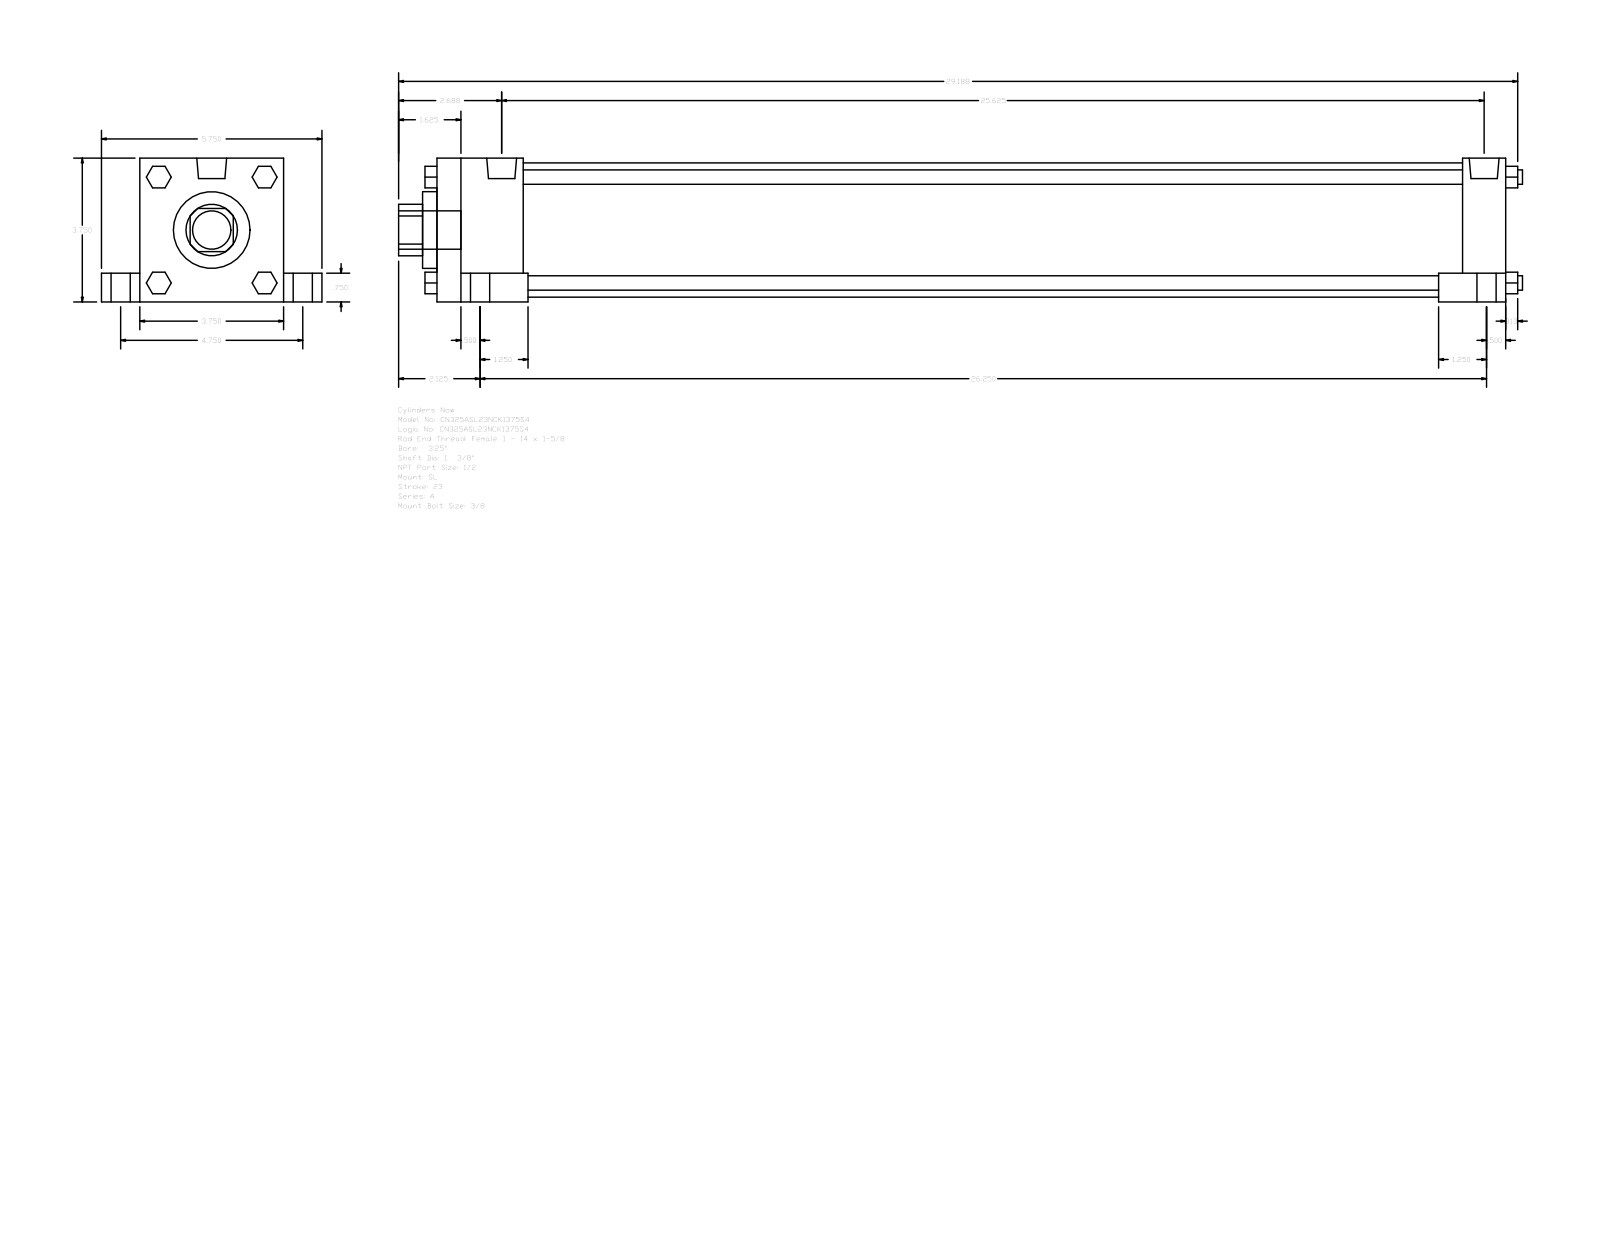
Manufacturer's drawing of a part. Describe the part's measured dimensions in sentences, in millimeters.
The part is named "A_SL__0325_1.375". Its 3-D file was written by "GSSL Pune (CONFIG_CONTROL_DESIGN)". It is 0 solids with 150 faces: 114 planar, 36 cylindrical and 0 other. Overall it measures 744.54 by 146.05 by 95.25 millimeters. Round holes: 1 of diameter 34.92, 1 of diameter 50.8, 1 of diameter 88.9. Round bosses or shafts: 4 of diameter 19.05, 4 of diameter 12.7, 4 of diameter 9.53, 4 of diameter 8.73, 2 of diameter 19.77, 1 of diameter 25.4. Partial cylindrical surfaces (rounded edges, fillets, slot ends): 1 of radius 17.06. The main face-to-face distances are 95.24, 708.02, 25.41, 120.65, 19.05, 76.19, 15.87, 28.57, 57.15, 679.45.
